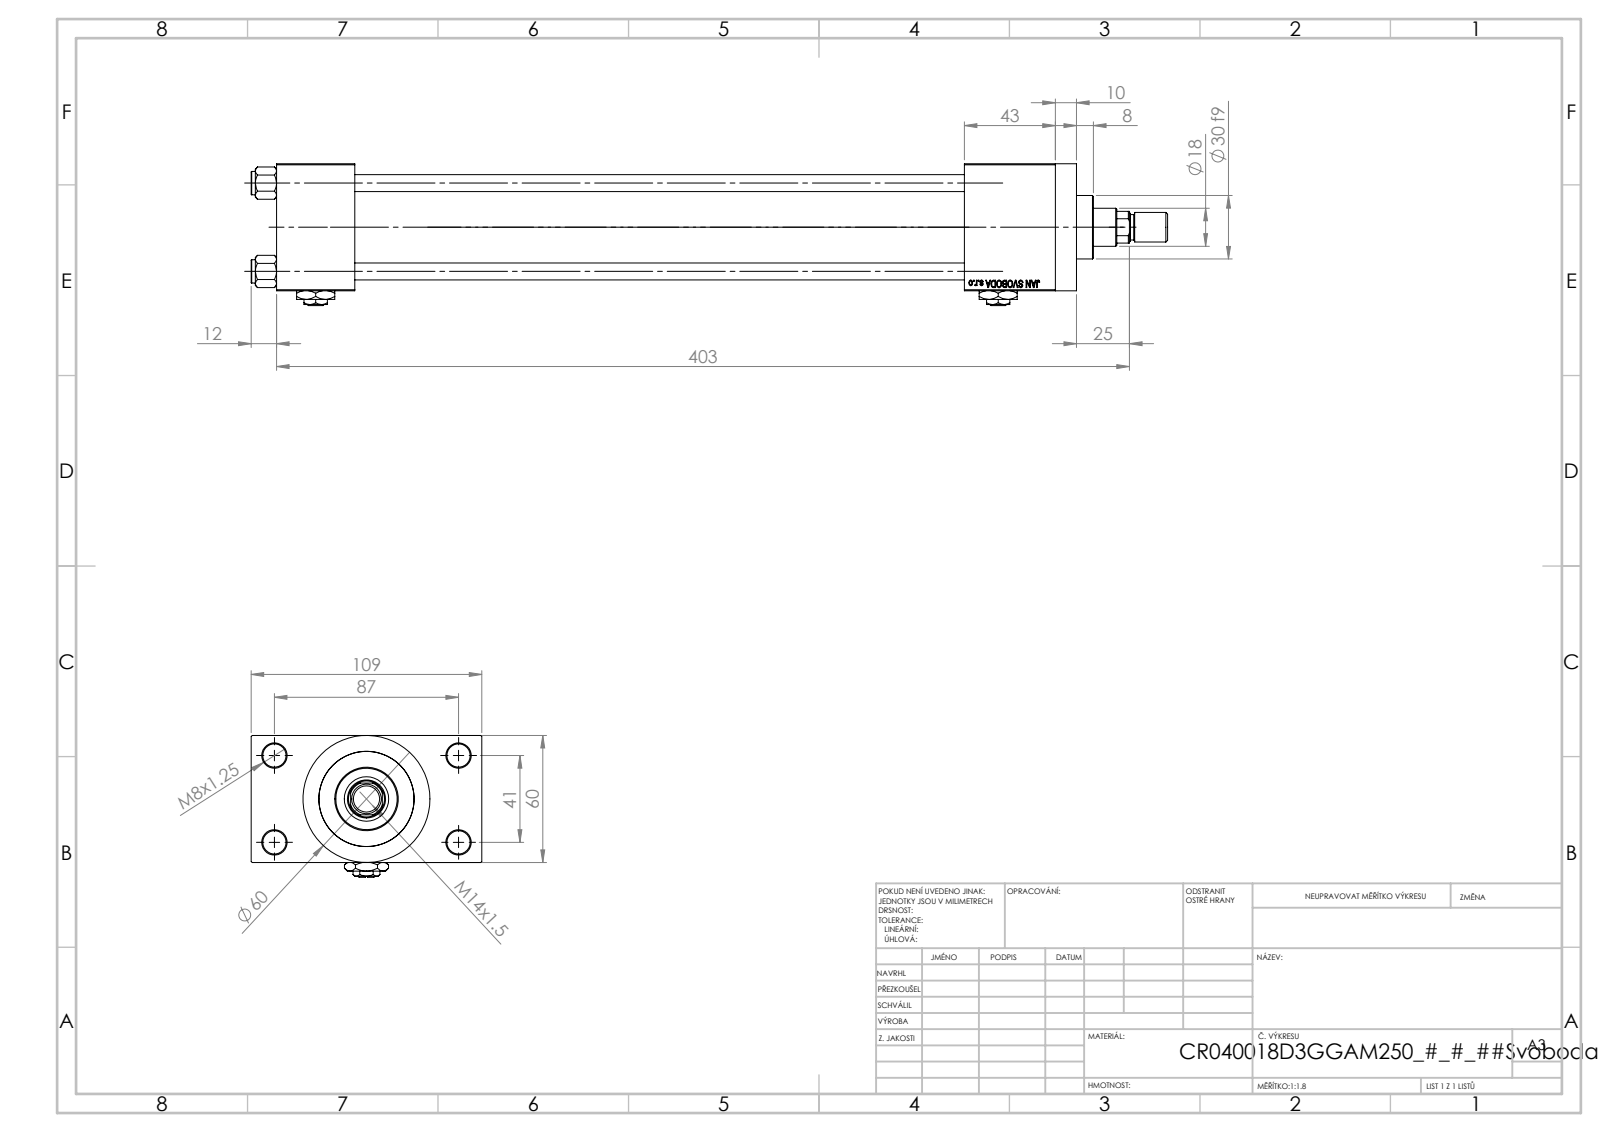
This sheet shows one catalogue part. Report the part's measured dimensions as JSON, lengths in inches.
{"part_name": "V215_VC_A; ROD_END_AH; NUT_M5_D; Zatka_pro_OIL_PORT (+3 more)", "step_written_by": "SolidWorks 2019 (CONFIG_CONTROL_DESIGN)", "units": "inches", "bodies": {"solids": 14, "faces": 1220, "planar": 550, "cylindrical": 104, "other": 566}, "overall_size": [17.047, 4.291, 2.638], "volume_in3": 43.71, "surface_area_in2": 346.1, "round_holes": [[0.315, 4], [0.433, 4], [0.276, 2], [0.656, 2], [0.945, 2], [0.335, 1], [0.709, 1], [0.827, 1], [1.22, 1], [1.575, 1], [1.772, 1]], "round_bosses_or_shafts": [[0.433, 4], [2.362, 1], [1.811, 1], [1.181, 1], [0.551, 1], [0.472, 1]], "partial_cylinders_radius": [[0.335, 1]], "face_to_face_distances": [2.362, 0.965, 3.327, 11.339, 1.457, 12.795, 1.693, 14.488, 13.031, 4.291], "hole_center_spacings": [0.892, 1.161, 1.642, 1.856, 1.893, 2.533, 3.011, 1.614]}
